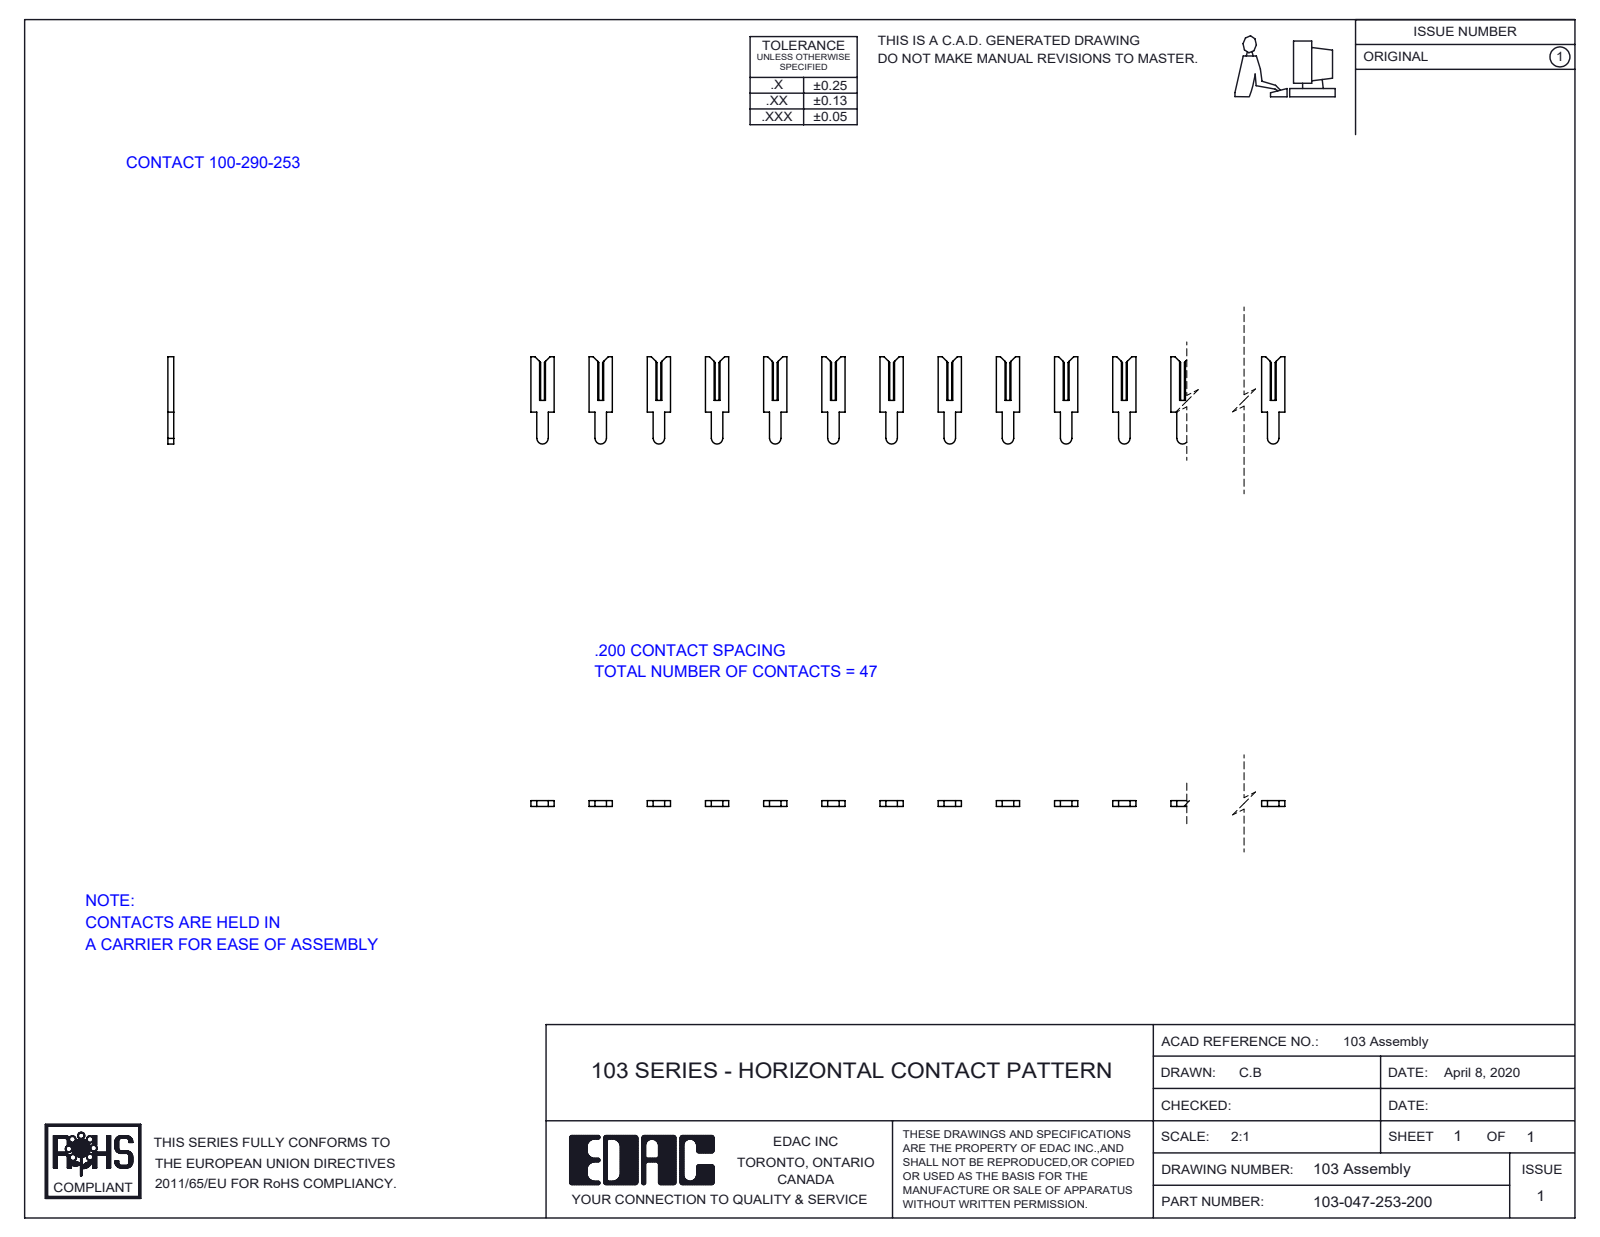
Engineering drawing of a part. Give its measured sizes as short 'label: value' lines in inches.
name: 103-047-253-200; 100-290-001_100-290-253
written by: SolidWorks 2016 (CONFIG_CONTROL_DESIGN)
unit: in
bodies: 47 solids, 940 faces (893 planar, 47 cylindrical, 0 other)
size: 9.28 × 0.3 × 0.02
volume: 0.016 in³; area: 2.507 in²
rounds: 47× R0.019
face distances: 0.02, 0.2, 0.4, 0.141, 0.6, 0.848, 0.283, 0.8, 0.99, 0.707
